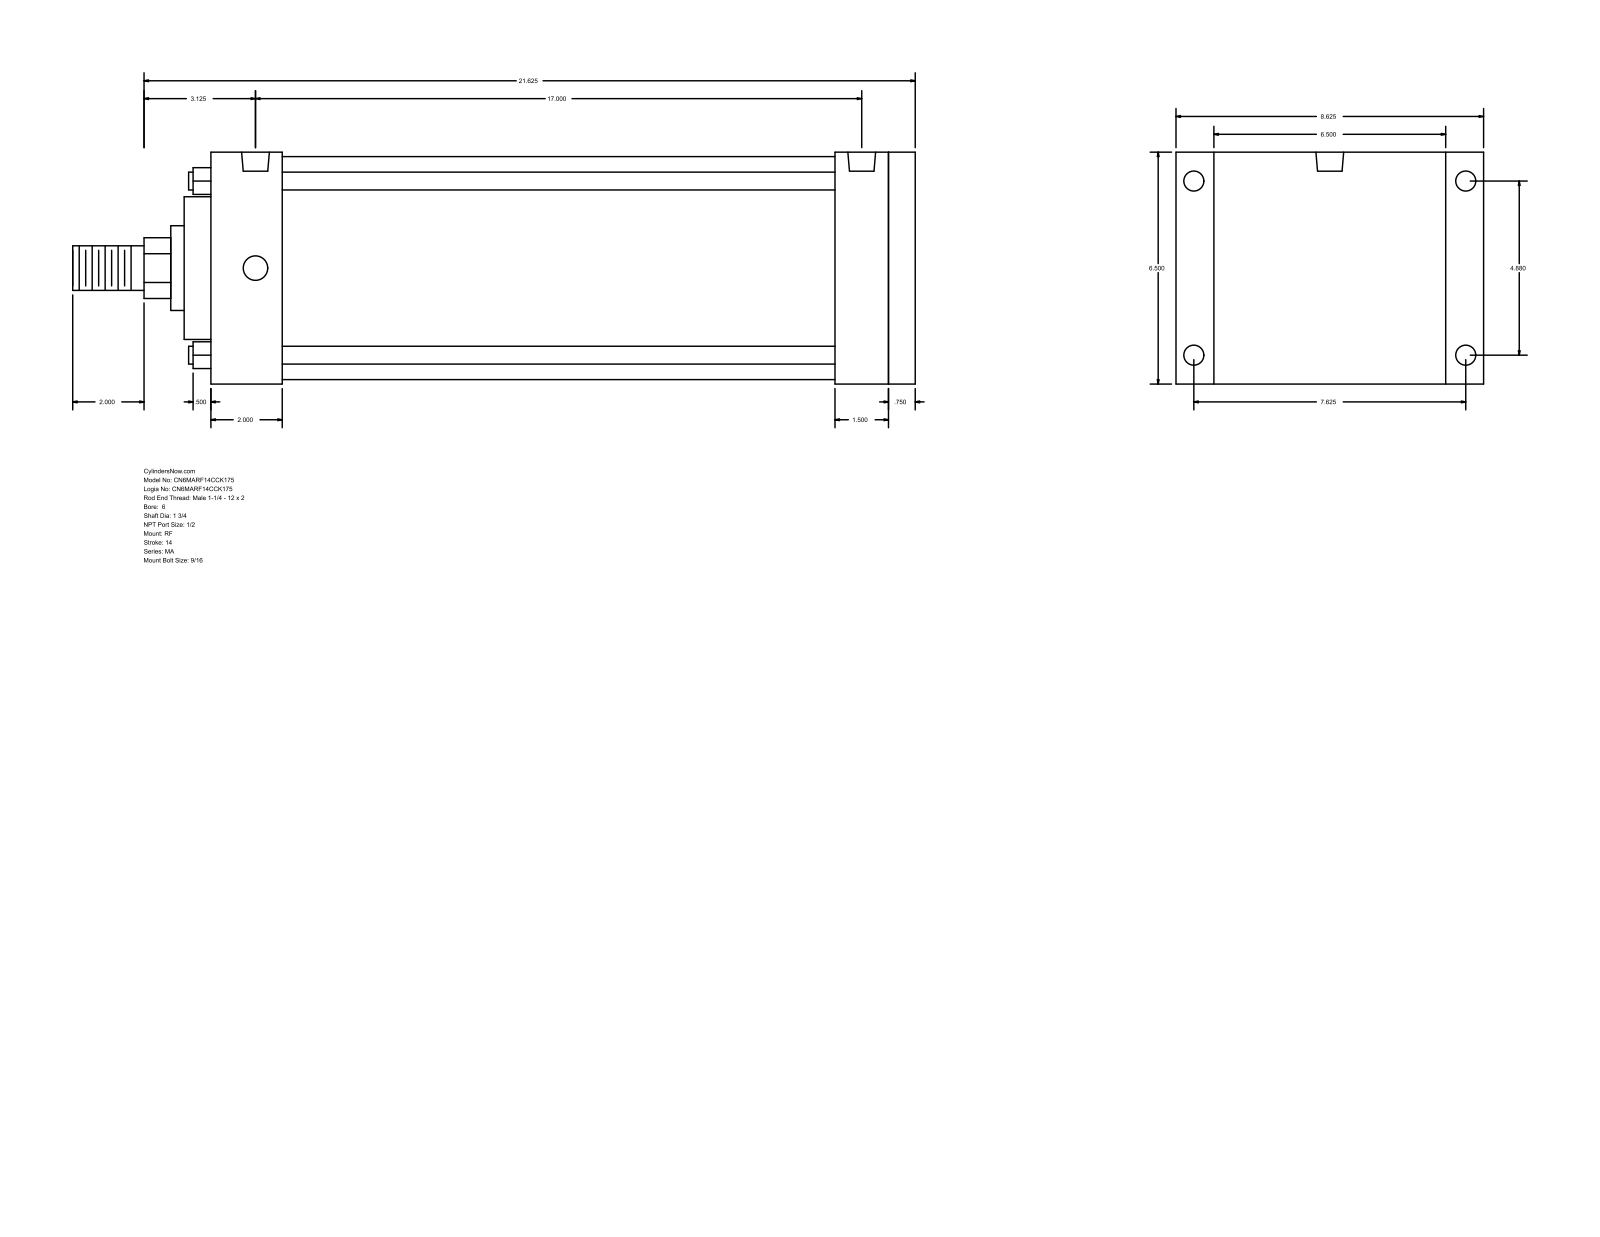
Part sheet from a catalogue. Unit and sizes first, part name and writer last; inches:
Units: inches
Overall size (bounding box): 23.625 × 8.625 × 6.5
Round holes (diameter × count): ⌀0.563 ×4, ⌀0.687 ×4, ⌀0.778 ×2
Round bosses / shafts (diameter × count): ⌀0.5 ×4, ⌀6.25 ×1, ⌀4 ×1, ⌀2.375 ×1, ⌀1.75 ×1, ⌀1.25 ×1
Partial cylindrical surfaces — rounded edges, fillets, slot ends (radius × count): R0.852 ×1
Main face-to-face distances: 6.5, 19.75, 0.75, 19, 2, 0.75, 17, 17.75, 17.5, 15.5
Hole centre spacings: 4.88, 7.625, 9.053, 17
Bodies: 0 solids, 94 faces (65 planar, 29 cylindrical, 0 other)
Part name (STEP PRODUCT): MA_RF__0600_1.75
STEP written by: GSSL Pune (CONFIG_CONTROL_DESIGN)
